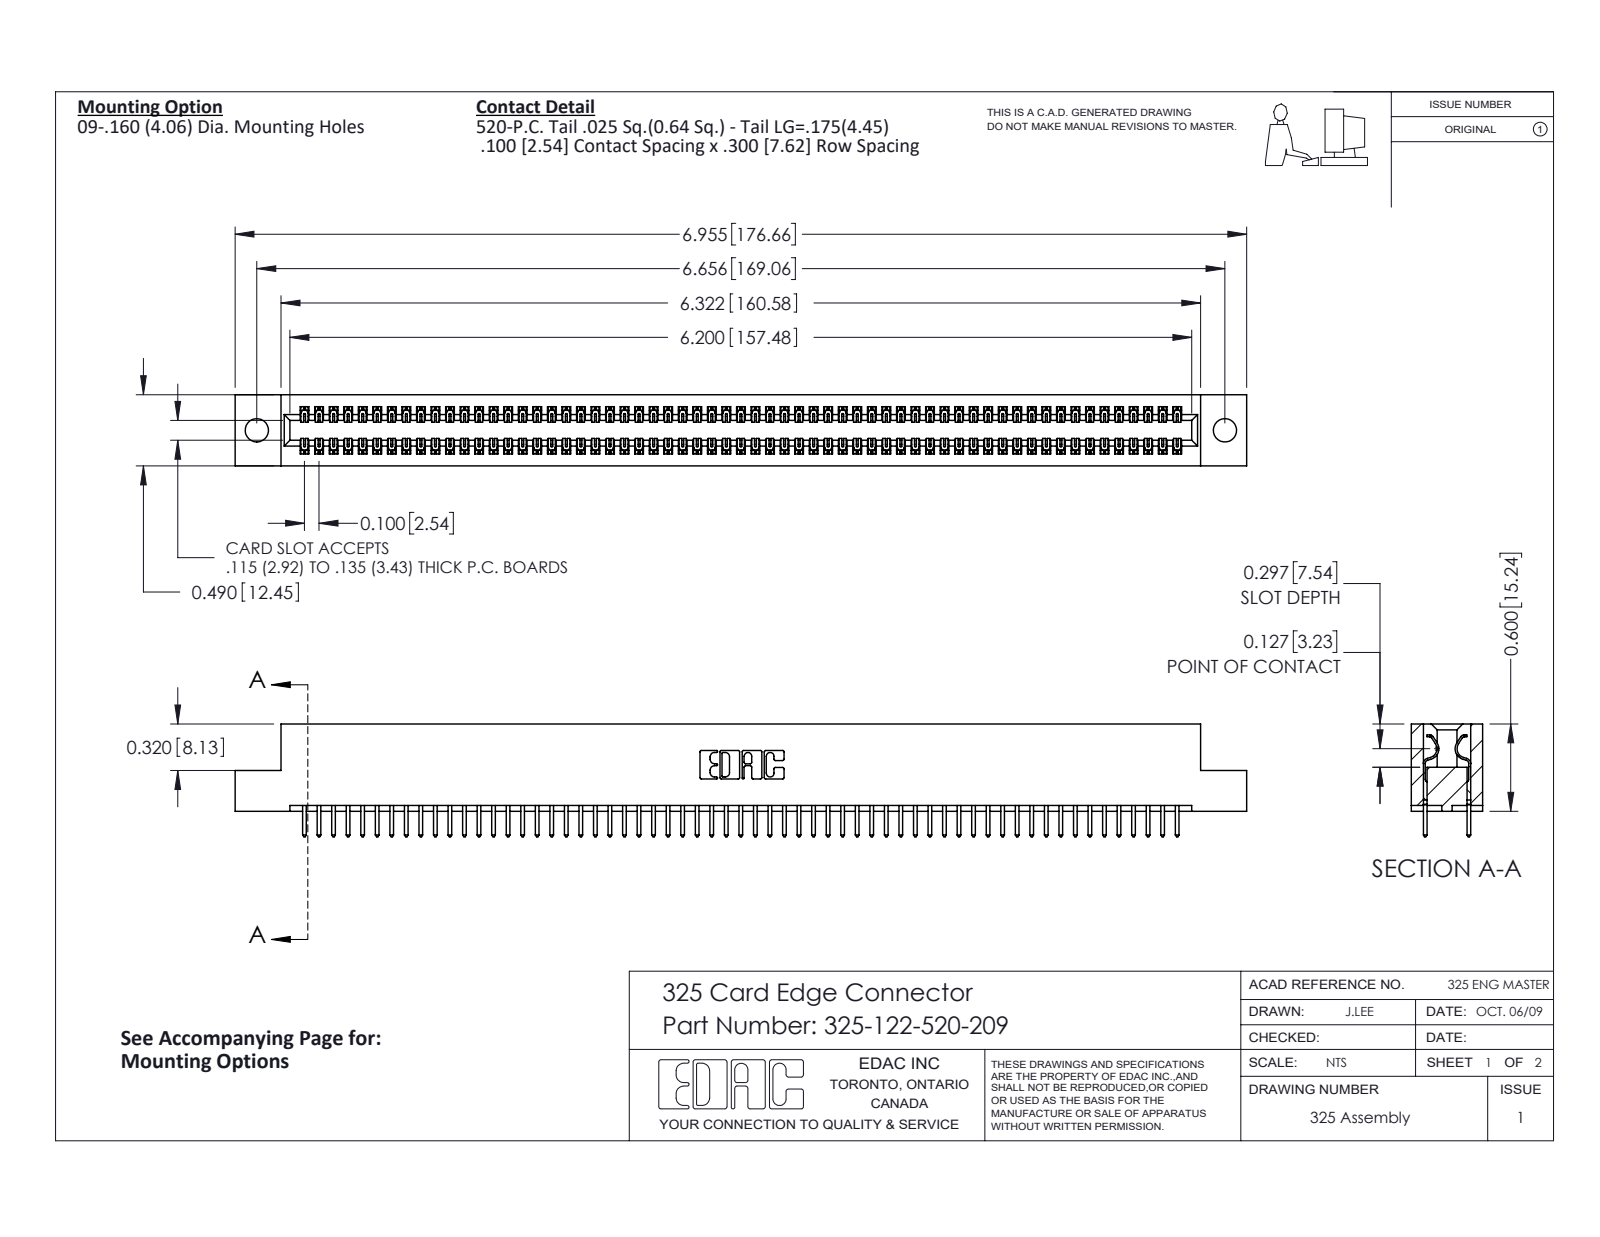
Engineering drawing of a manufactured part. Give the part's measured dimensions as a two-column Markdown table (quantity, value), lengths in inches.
| quantity | value |
| --- | --- |
| part name | 325-122-520-209; 325 Part_.160 TH; 325-292-001_325-293-120 |
| STEP written by | SolidWorks 2016 (CONFIG_CONTROL_DESIGN) |
| units | inches |
| bodies | 123 solids, 6458 faces (4462 planar, 1996 cylindrical, 0 other) |
| overall size | 6.955 × 0.775 × 0.49 |
| volume | 1.387 in³ |
| surface area | 42.83 in² |
| round holes (diameter × count) | 0.16 × 2 |
| partial cylindrical surfaces (radius × count) | 0.006 × 183, 0.01 × 122, 0.01 × 22, 0.007 × 6, 0.031 × 6, 0.026 × 3, 0.014 × 2, 0.022 × 2 |
| main face-to-face distances | 0.083, 0.407, 0.49, 0.107, 0.383, 0.025, 0.3, 0.325, 0.275, 0.263 |
| hole center spacings | 6.656 |
